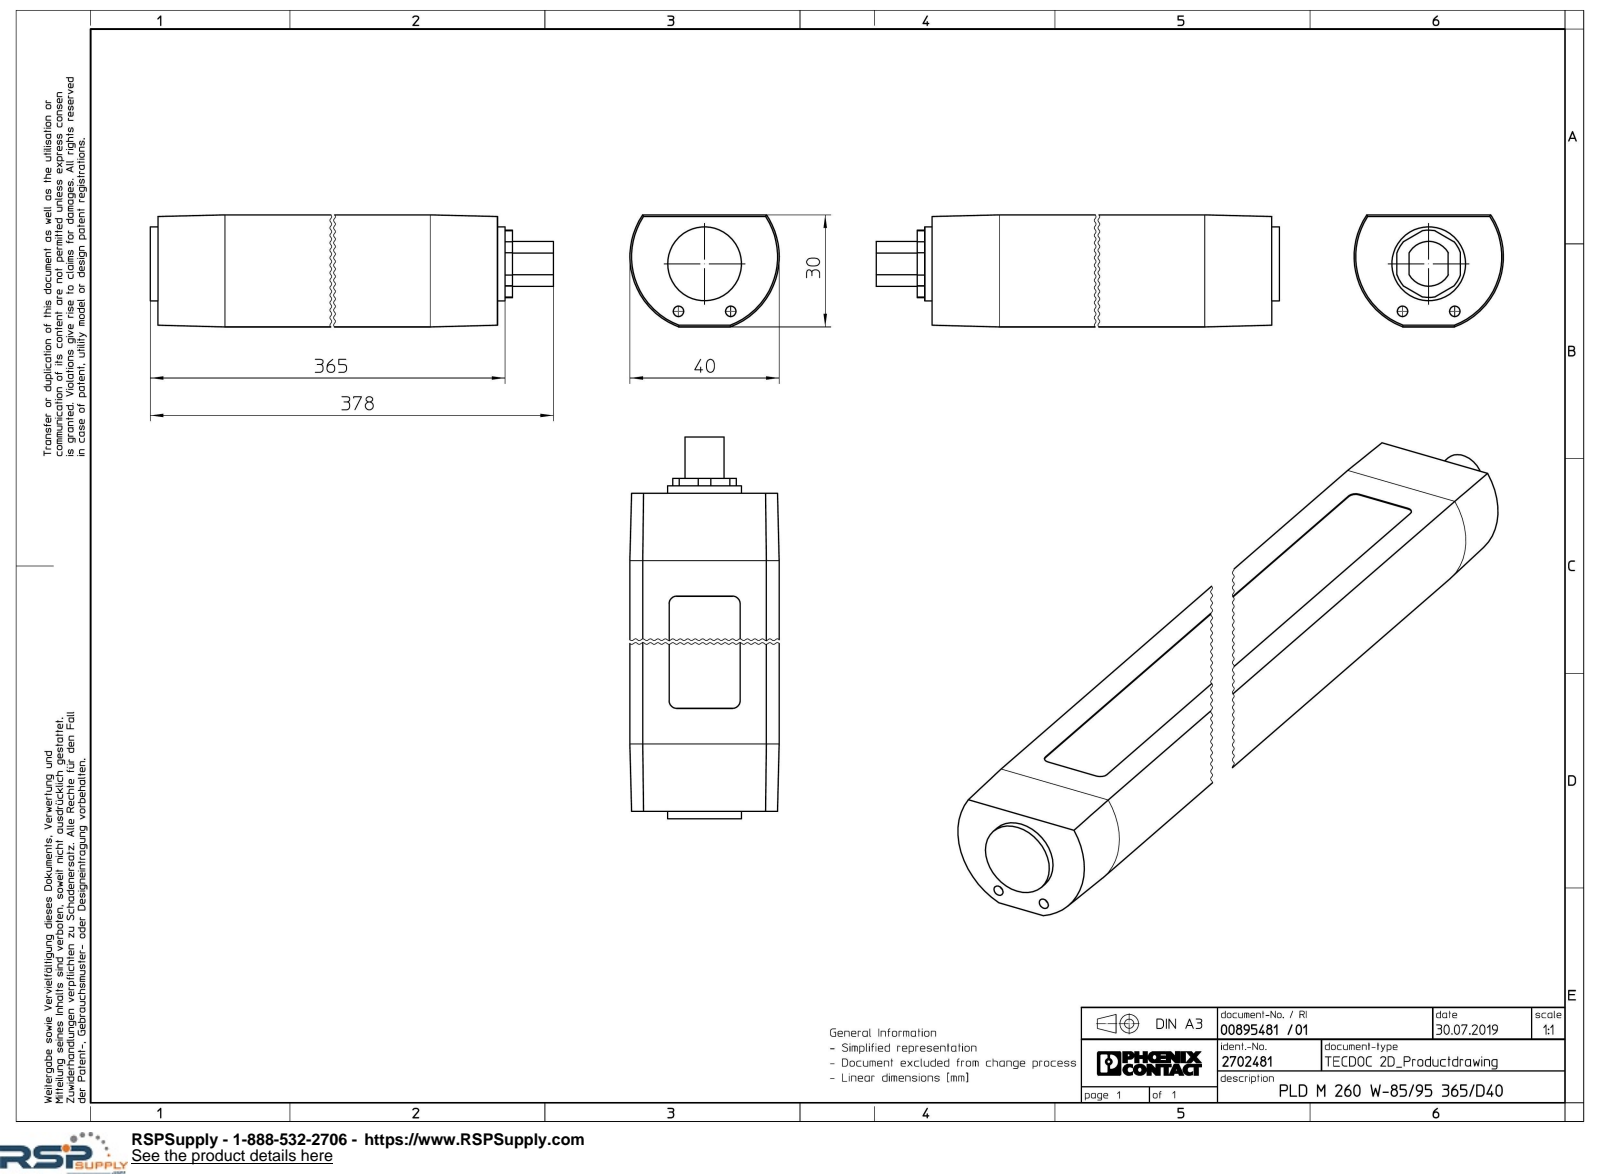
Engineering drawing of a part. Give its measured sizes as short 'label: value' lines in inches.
name: PLD_M_260_W_85_95_365_D40-select
written by: Creo Elements/Direct Modeling 20.1A 29-Sep-2018 (C) Parametric Technology GmbH (AUTOMOTIVE_DESIGN)
unit: in
bodies: 1 solid, 59 faces (29 planar, 26 cylindrical, 4 other)
size: 14.882 × 1.575 × 1.179
volume: 22.95 in³; area: 71.38 in²
holes: 2× ⌀0.11
bosses: 1× ⌀0.778
rounds: 4× R0.079, 1× R0.236, 1× R0.354, 1× R0.787
face distances: 1.171, 1.179, 14.213, 1.486, 0.079, 14.291, 14.37, 0.157, 14.449, 0.167
hole spacings: 0.551
